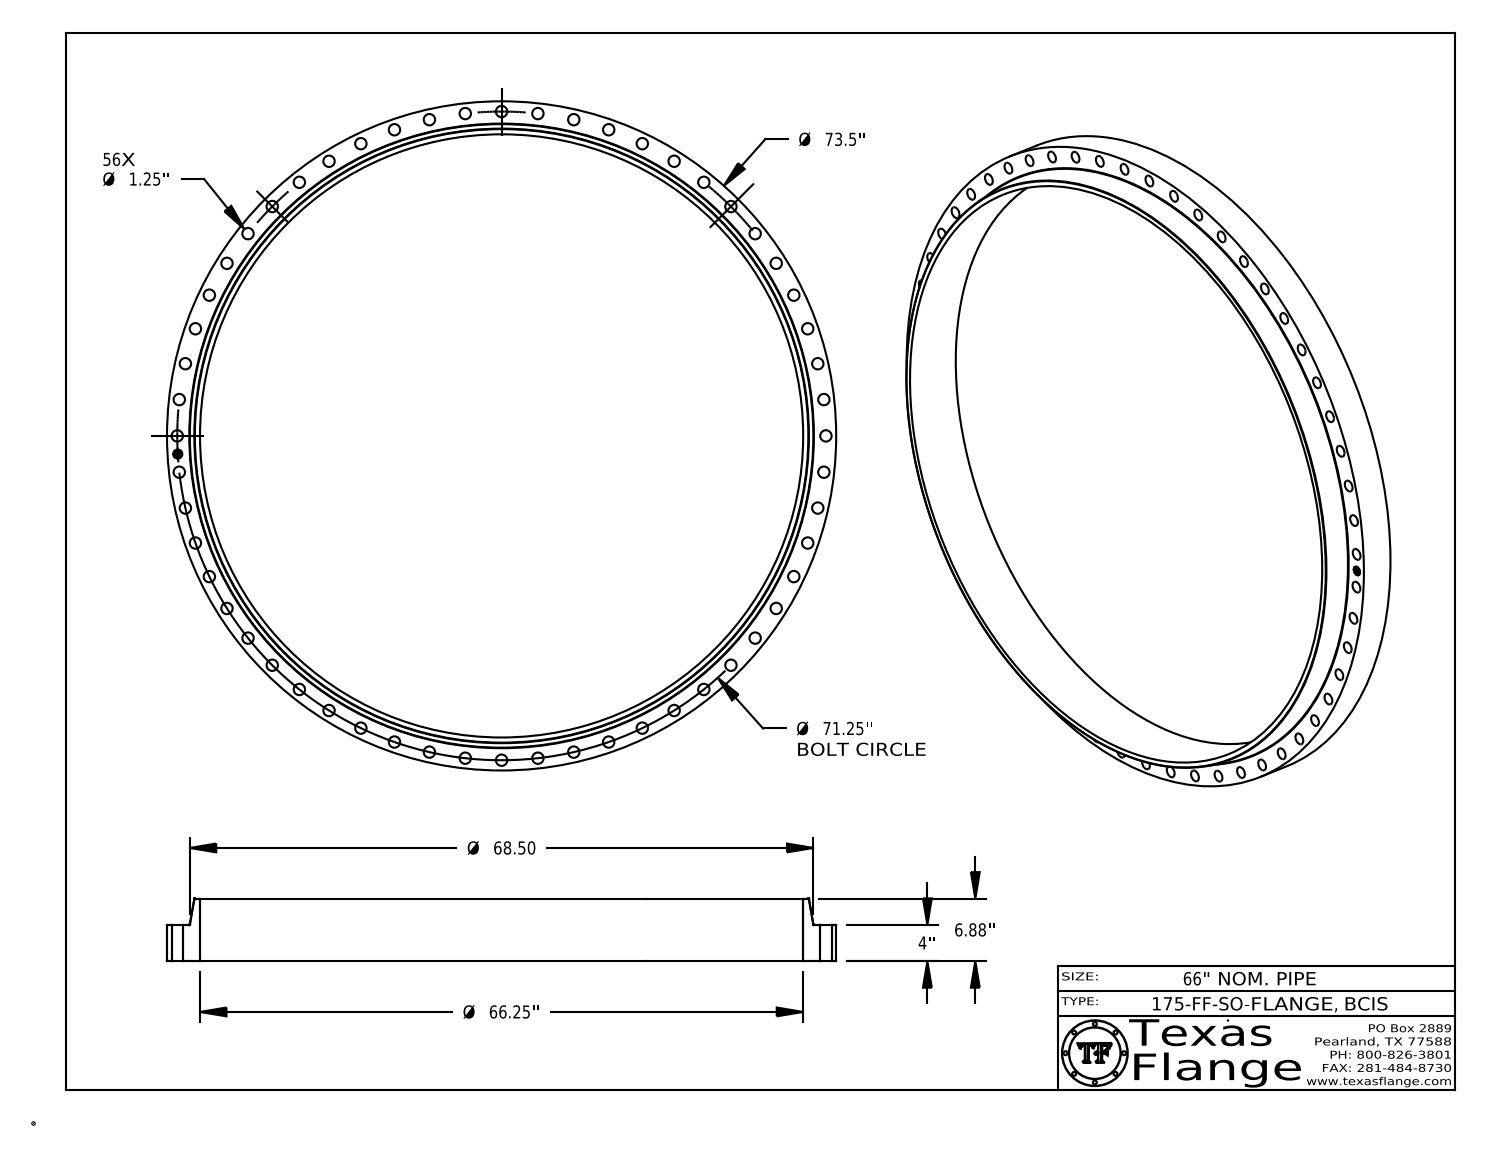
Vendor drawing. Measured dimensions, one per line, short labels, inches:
name: BCIS, Class 175-FF-SO
written by: CATIA V5 STEP AP214 (AUTOMOTIVE_DESIGN)
unit: in
bodies: 1 solid, 510 faces (368 planar, 136 cylindrical, 6 other)
size: 73.5 × 73.5 × 6.88
volume: 3 437 in³; area: 5 198 in²
holes: 56× ⌀1.25, 1× ⌀1, 1× ⌀66.25
bosses: 8× ⌀0.061, 1× ⌀73.5, 1× ⌀0.788
face distances: 4, 6.88, 2.88, 0.015, 3.985, 2.895, 0.298, 0.292, 0.055, 0.193
hole spacings: 7.978, 15.855, 68.465, 71.138, 11.935, 35.625, 70.243, 3.995
